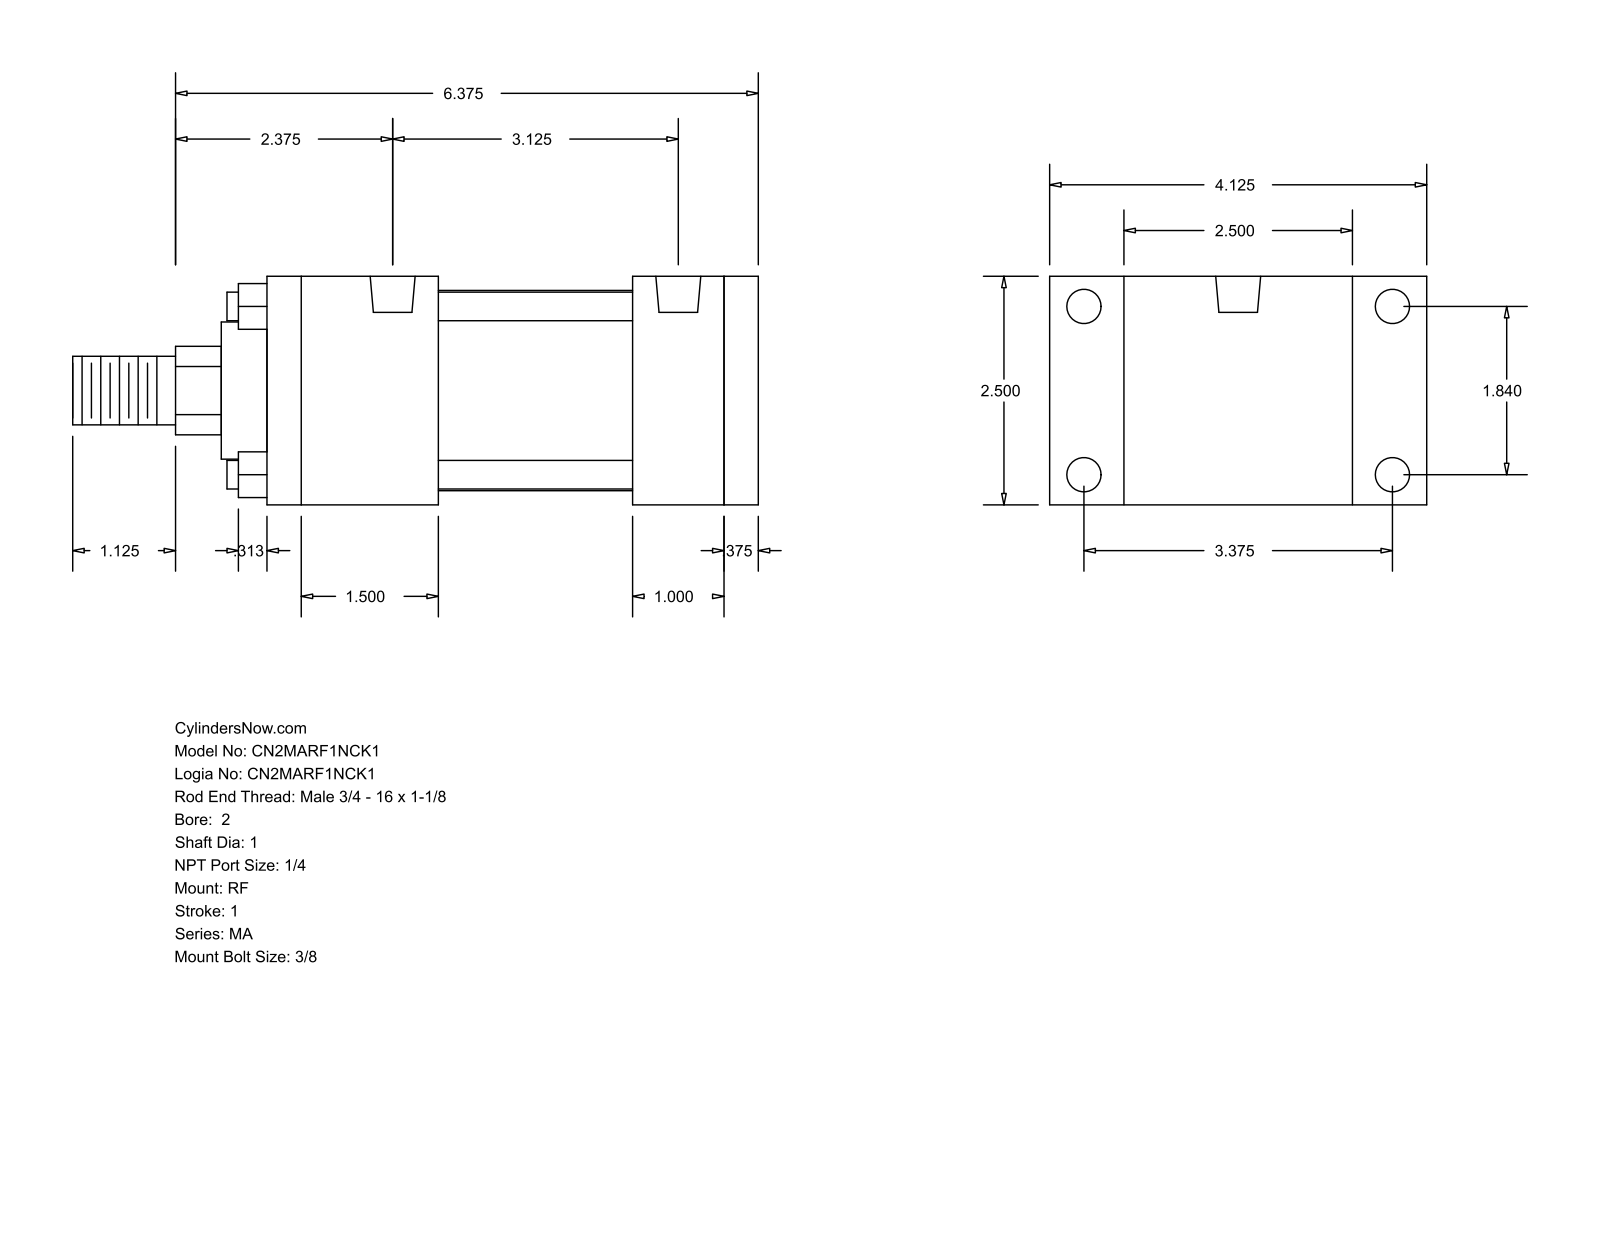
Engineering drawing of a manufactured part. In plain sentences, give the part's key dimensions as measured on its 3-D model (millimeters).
The part is named "MA_RF__0200_1". Its 3-D file was written by "GSSL Pune (CONFIG_CONTROL_DESIGN)". It is 0 solids with 92 faces: 64 planar, 28 cylindrical and 0 other. Overall it measures 190.5 by 104.78 by 63.5 millimeters. Round holes: 4 of diameter 7.94, 4 of diameter 9.53, 2 of diameter 12.49. Round bosses or shafts: 4 of diameter 7.94, 1 of diameter 55.63, 1 of diameter 38.1, 1 of diameter 25.4, 1 of diameter 19.05. Partial cylindrical surfaces (rounded edges, fillets, slot ends): 1 of radius 12.29. The main face-to-face distances are 63.5, 127, 9.53, 136.53, 53.97, 101.6, 25.4, 20.64, 12.7, 47.63. The hole center spacings are 46.74, 79.37, 85.72, 97.63.
